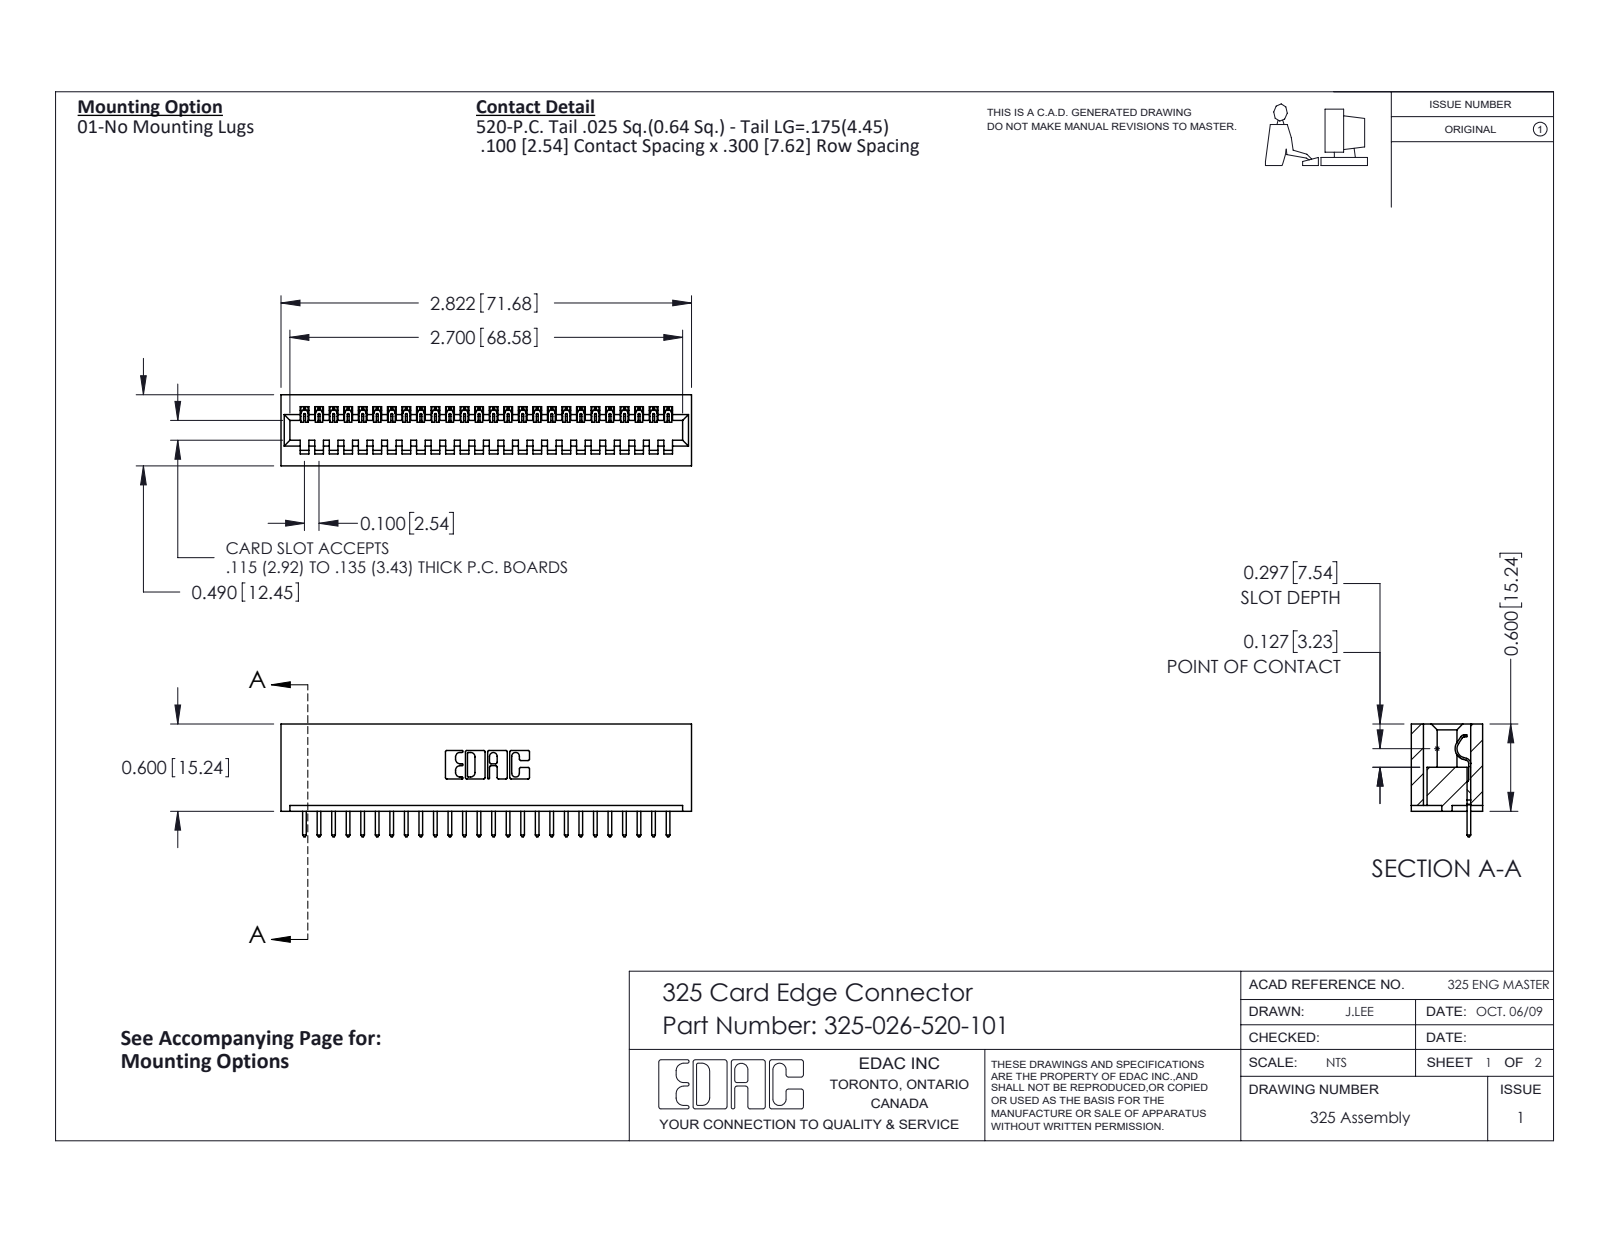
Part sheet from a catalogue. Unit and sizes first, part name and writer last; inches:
Units: inches
Overall size (bounding box): 2.822 × 0.775 × 0.49
Partial cylindrical surfaces — rounded edges, fillets, slot ends (radius × count): R0.006 ×52, R0.01 ×52, R0.01 ×22, R0.007 ×6, R0.031 ×6, R0.026 ×3, R0.014 ×1, R0.022 ×1
Main face-to-face distances: 0.083, 0.407, 0.3, 0.49, 0.107, 0.383, 0.025, 0.325, 0.56, 0.1
Volume: 0.578 in³ · Surface area: 15.97 in²
Bodies: 27 solids, 1614 faces (1158 planar, 456 cylindrical, 0 other)
Part name (STEP PRODUCT): 325-292-001_325-293-120; 325 Part_Lugless; 325-026-520-101
STEP written by: SolidWorks 2016 (CONFIG_CONTROL_DESIGN)
